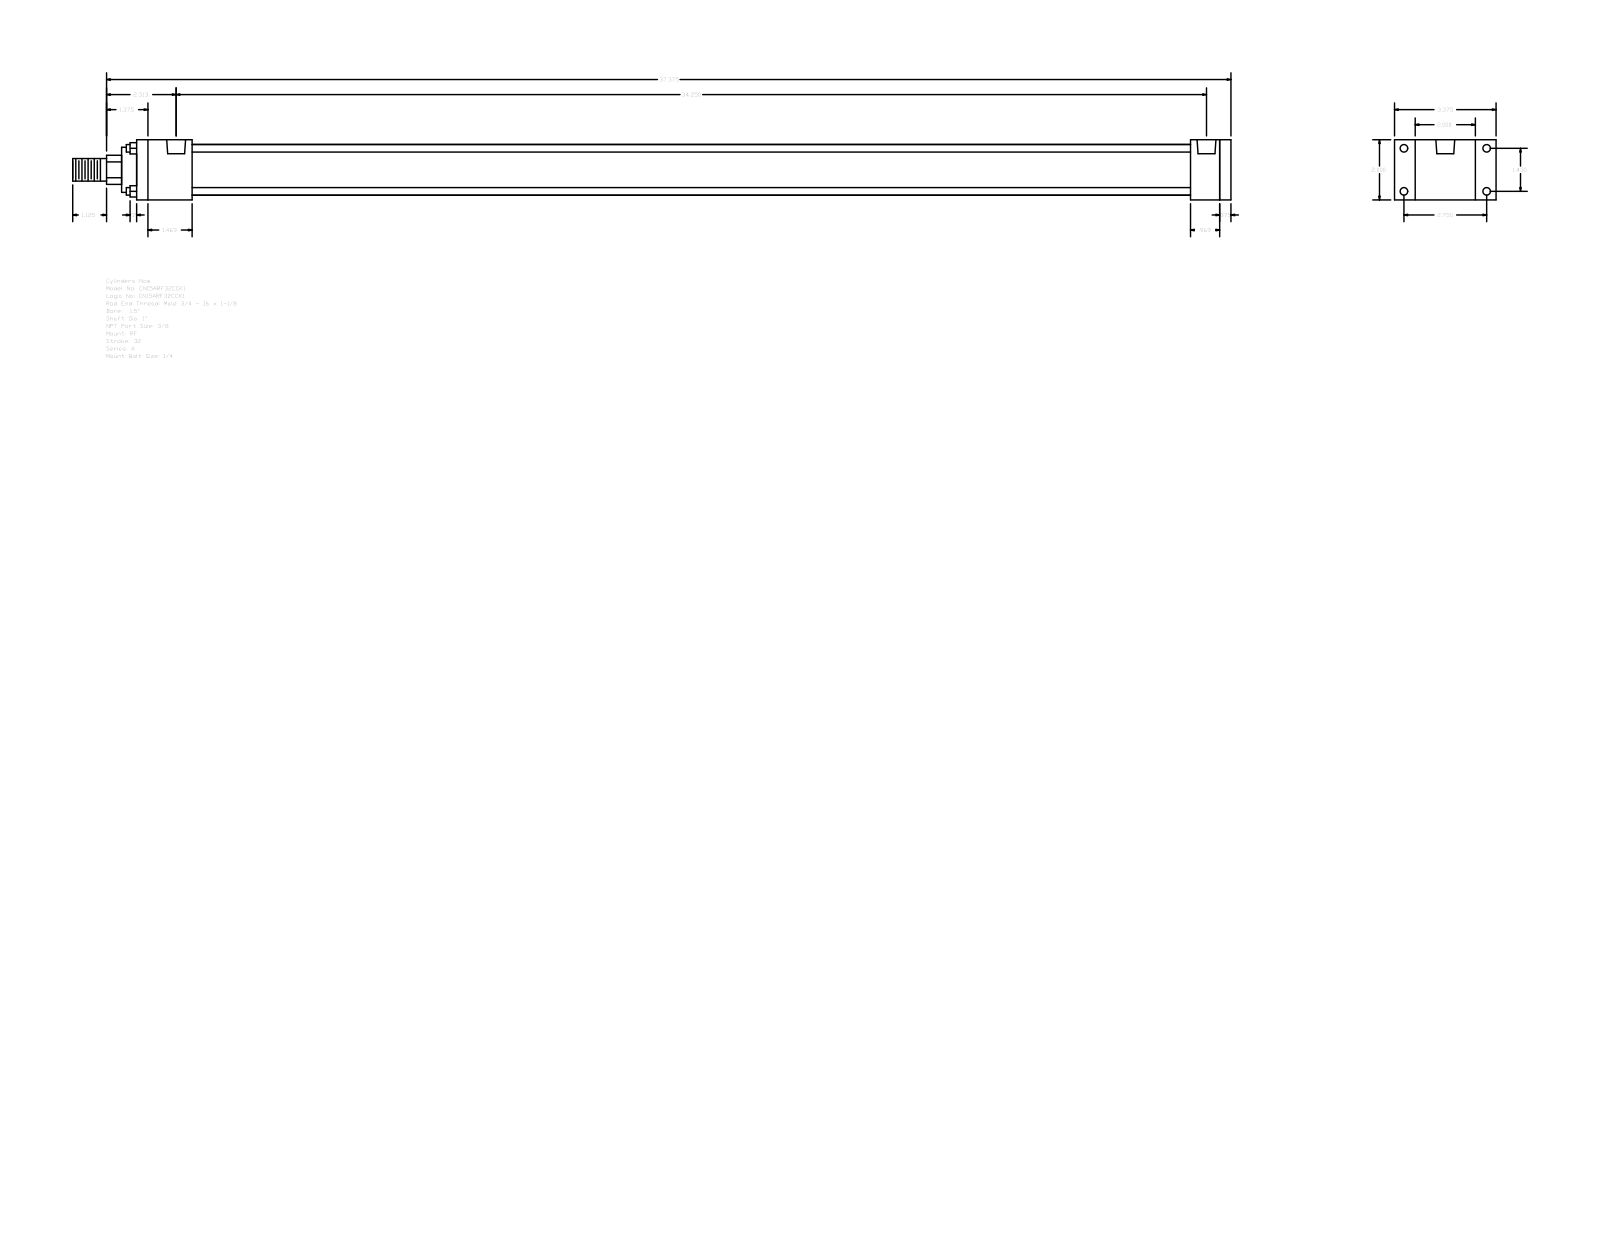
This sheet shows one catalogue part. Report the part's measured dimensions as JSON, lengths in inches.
{"part_name": "A_RF__0150_1", "step_written_by": "GSSL Pune (CONFIG_CONTROL_DESIGN)", "units": "inches", "bodies": {"solids": 0, "faces": 92, "planar": 64, "cylindrical": 28, "other": 0}, "overall_size": [38.5, 3.375, 2], "round_holes": [[0.219, 4], [0.25, 4], [0.627, 2]], "round_bosses_or_shafts": [[0.25, 4], [1.69, 1], [1.5, 1], [1, 1], [0.75, 1]], "partial_cylinders_radius": [[0.484, 1]], "face_to_face_distances": [2, 0.375, 36, 36.375, 35.031, 0.969, 1.344, 1.844, 33.187, 34.156], "hole_center_spacings": [0.156, 1.43, 2.75, 3.099, 33.937, 34.094, 34.25]}
